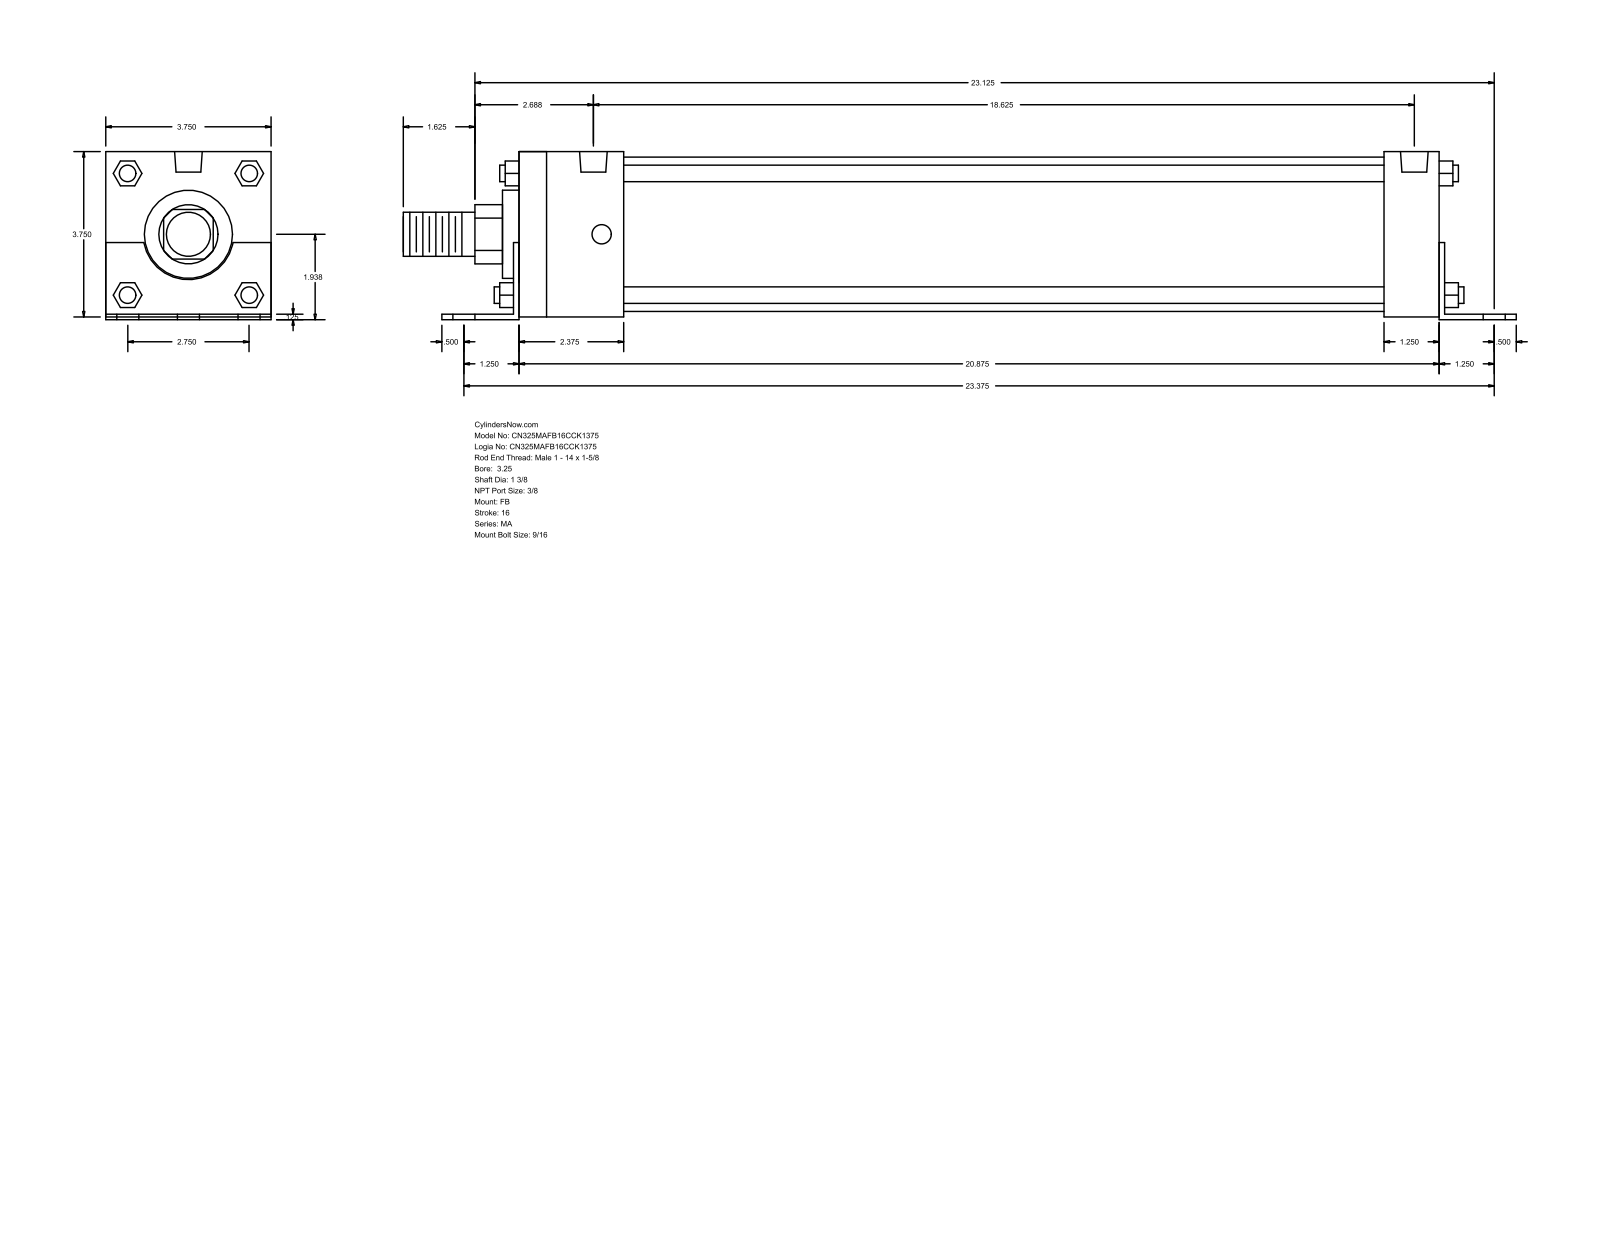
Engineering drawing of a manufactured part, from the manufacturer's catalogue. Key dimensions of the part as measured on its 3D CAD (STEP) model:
Part name (STEP PRODUCT): MA_FB__0325_1.375
STEP written by: GSSL Pune (CONFIG_CONTROL_DESIGN)
Units: millimetres
Bodies: 0 solids, 140 faces (105 planar, 35 cylindrical, 0 other)
Overall size (bounding box): 641.35 × 96.84 × 95.25
Round holes (diameter × count): ⌀14.29 ×6, ⌀11.11 ×4, ⌀15.93 ×2
Round bosses / shafts (diameter × count): ⌀9.53 ×4, ⌀88.9 ×1, ⌀50.8 ×1, ⌀34.92 ×1, ⌀25.4 ×1
Partial cylindrical surfaces — rounded edges, fillets, slot ends (radius × count): R17.06 ×1, R26.16 ×1
Main face-to-face distances: 95.24, 3.17, 1.59, 96.83, 1.58, 93.66, 3.18, 530.22, 533.4, 34.92
Hole centre spacings: 34.92, 594.76, 593.73, 57.78, 61.64, 69.84, 82.38, 86.72
